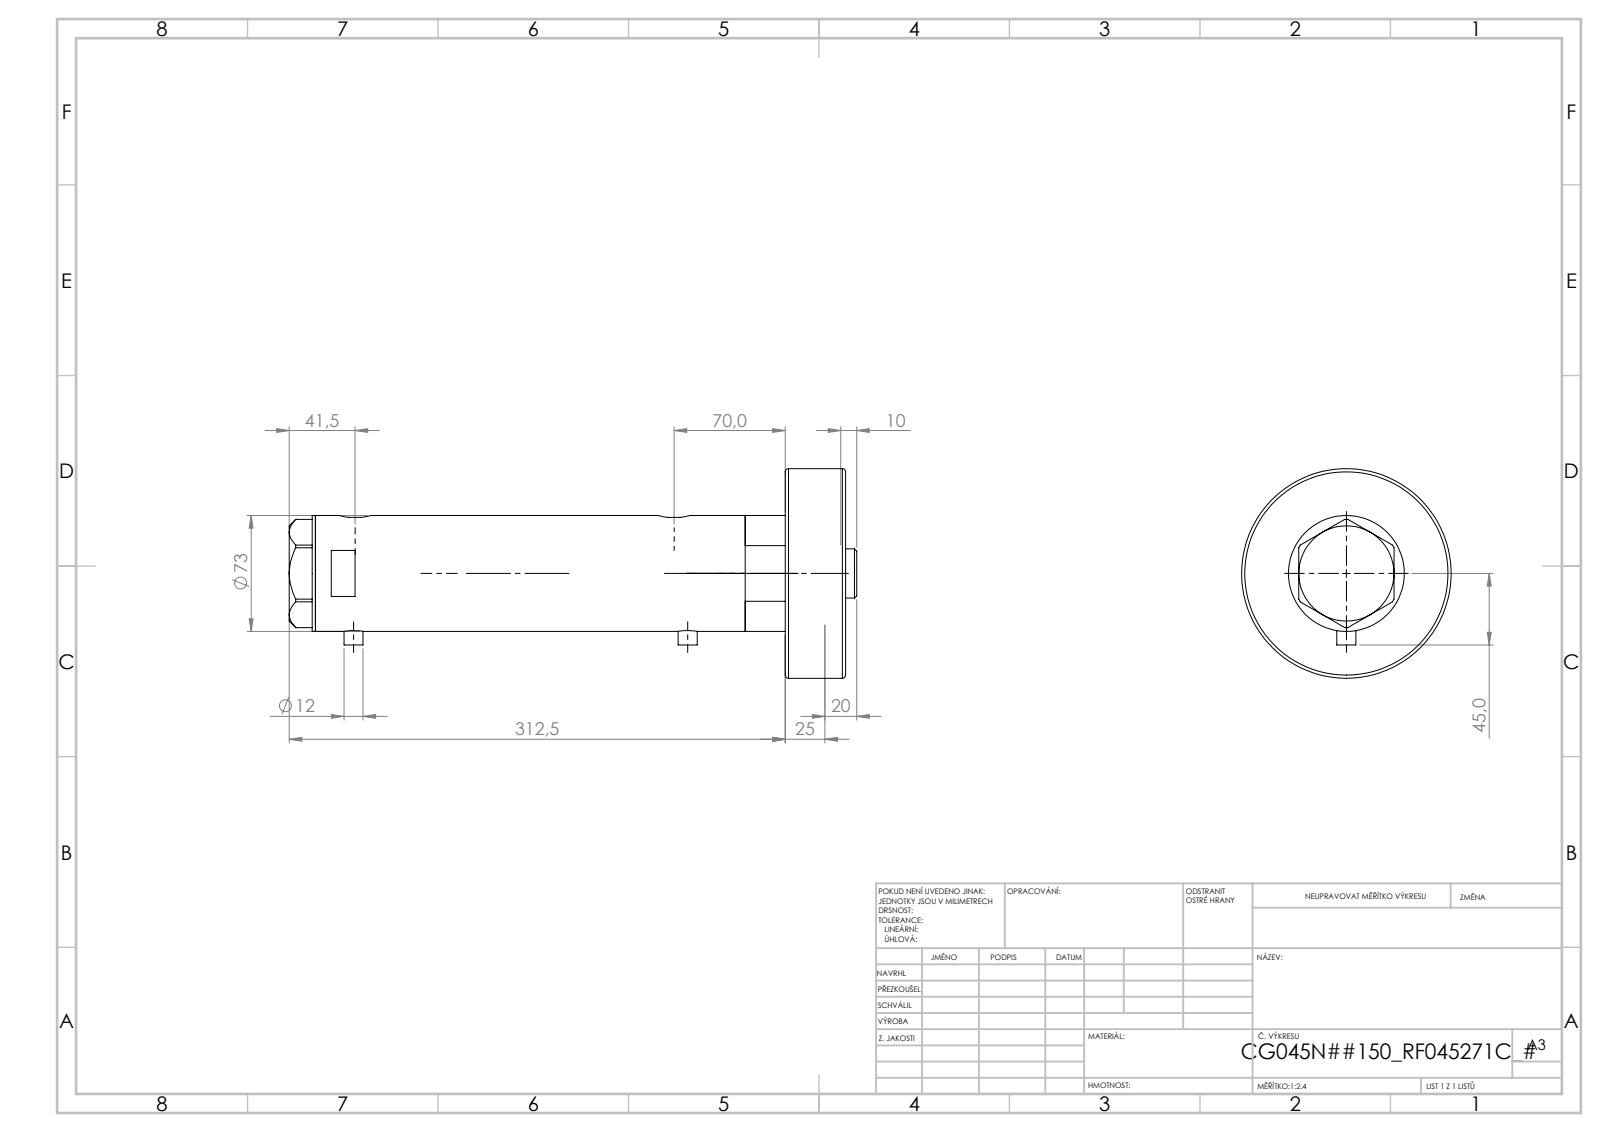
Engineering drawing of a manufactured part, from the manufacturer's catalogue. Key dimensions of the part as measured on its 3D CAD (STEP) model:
Part name (STEP PRODUCT): V270CG_271C; V270CG_BACK; V270CG_MIDDLE; V270CG_FRONT (+1 more)
STEP written by: SolidWorks 2019 (CONFIG_CONTROL_DESIGN)
Units: millimetres
Bodies: 5 solids, 130 faces (51 planar, 55 cylindrical, 24 other)
Overall size (bounding box): 357.5 × 132 × 132
Volume: 1 659 000 mm³ · Surface area: 242 555 mm²
Round holes (diameter × count): ⌀12.5 ×2, ⌀13.16 ×2, ⌀10.5 ×1, ⌀32 ×1, ⌀33.5 ×1, ⌀45 ×1, ⌀48 ×1, ⌀60 ×1, ⌀64 ×1
Round bosses / shafts (diameter × count): ⌀12 ×2, ⌀132 ×1, ⌀73 ×1, ⌀58 ×1, ⌀31 ×1
Partial cylindrical surfaces — rounded edges, fillets, slot ends (radius × count): R10 ×2
Main face-to-face distances: 38, 296, 334, 226, 70, 108, 26, 200, 270, 308
Hole centre spacings: 1, 8.5, 201, 202, 209.5, 210.5
